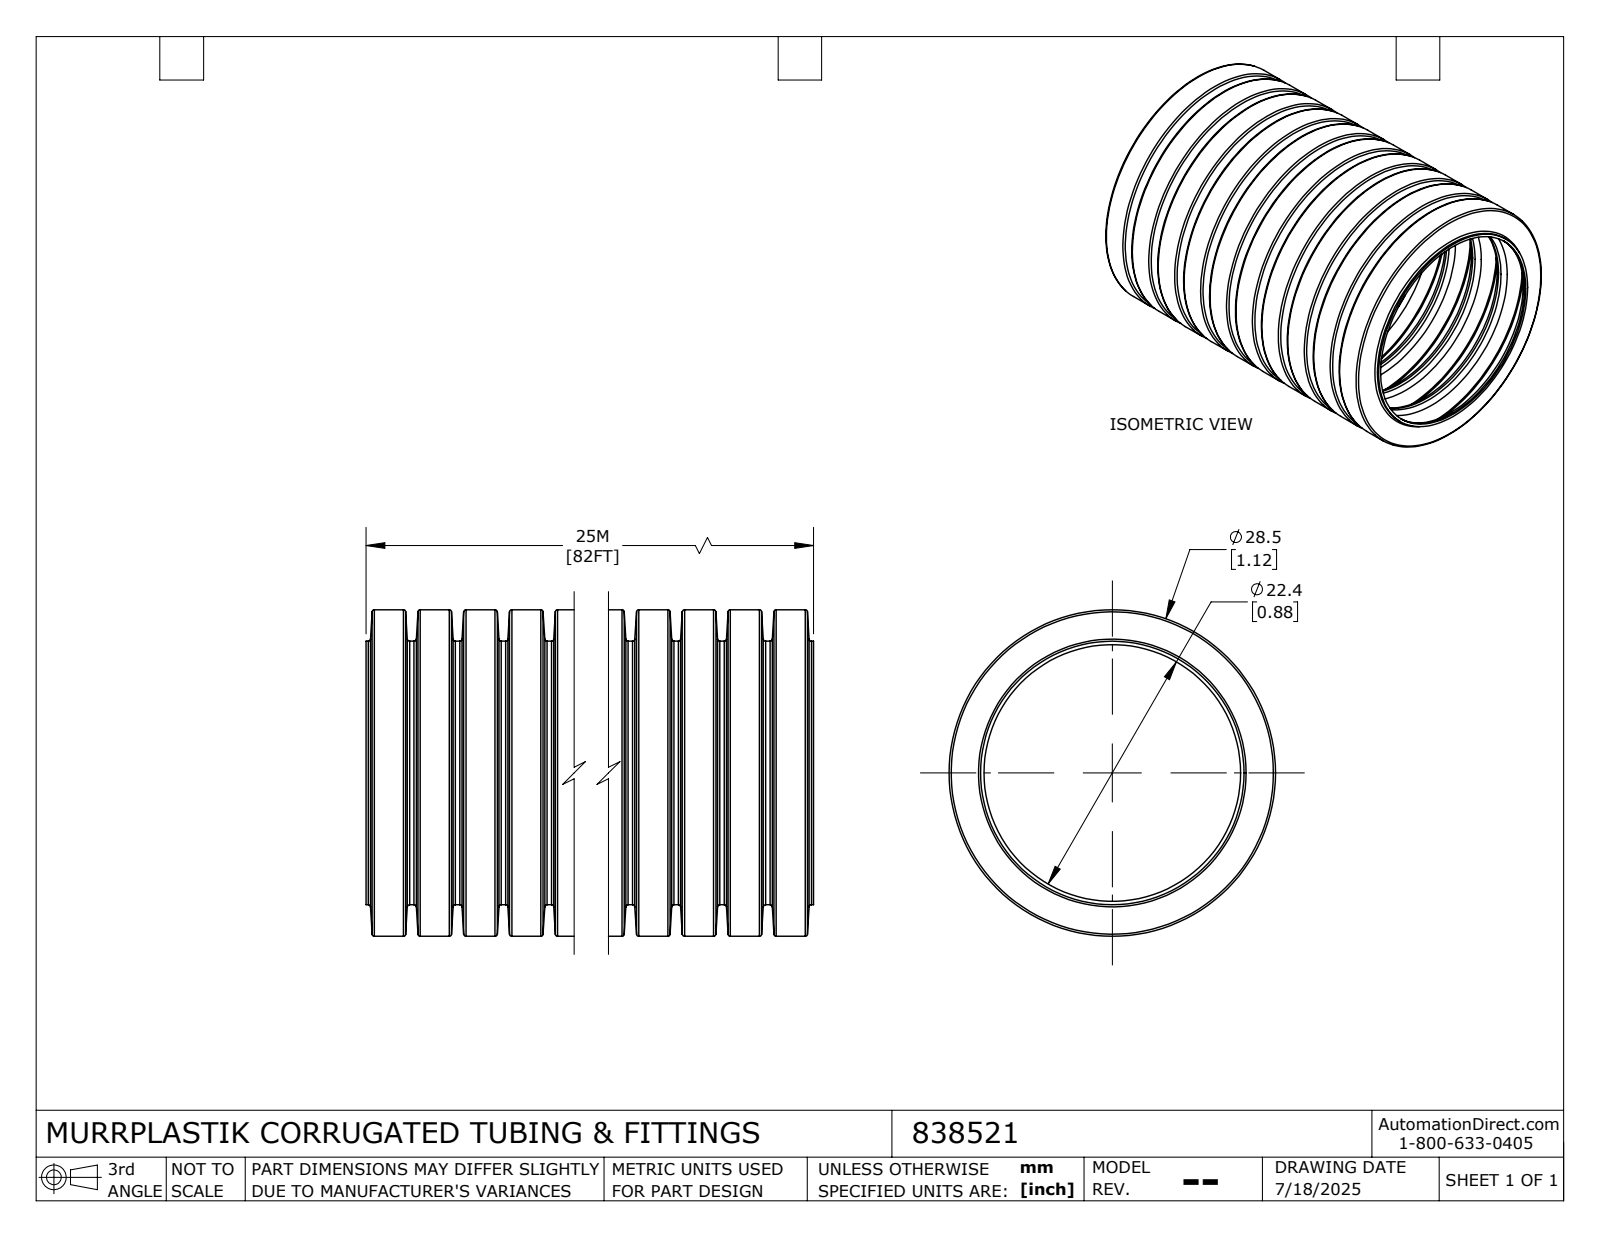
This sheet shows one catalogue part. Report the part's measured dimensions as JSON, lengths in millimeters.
{"part_name": "838521_Default", "step_written_by": "SolidWorks 2024 (CONFIG_CONTROL_DESIGN)", "units": "millimeters", "bodies": {"solids": 1, "faces": 164, "planar": 2, "cylindrical": 42, "other": 120}, "overall_size": [40, 28.5, 28.5], "volume_mm3": 2167, "surface_area_mm2": 14438, "round_holes": [[22.4, 1], [27.9, 1]], "round_bosses_or_shafts": [[28.5, 1], [23, 1]], "face_to_face_distances": [40]}
